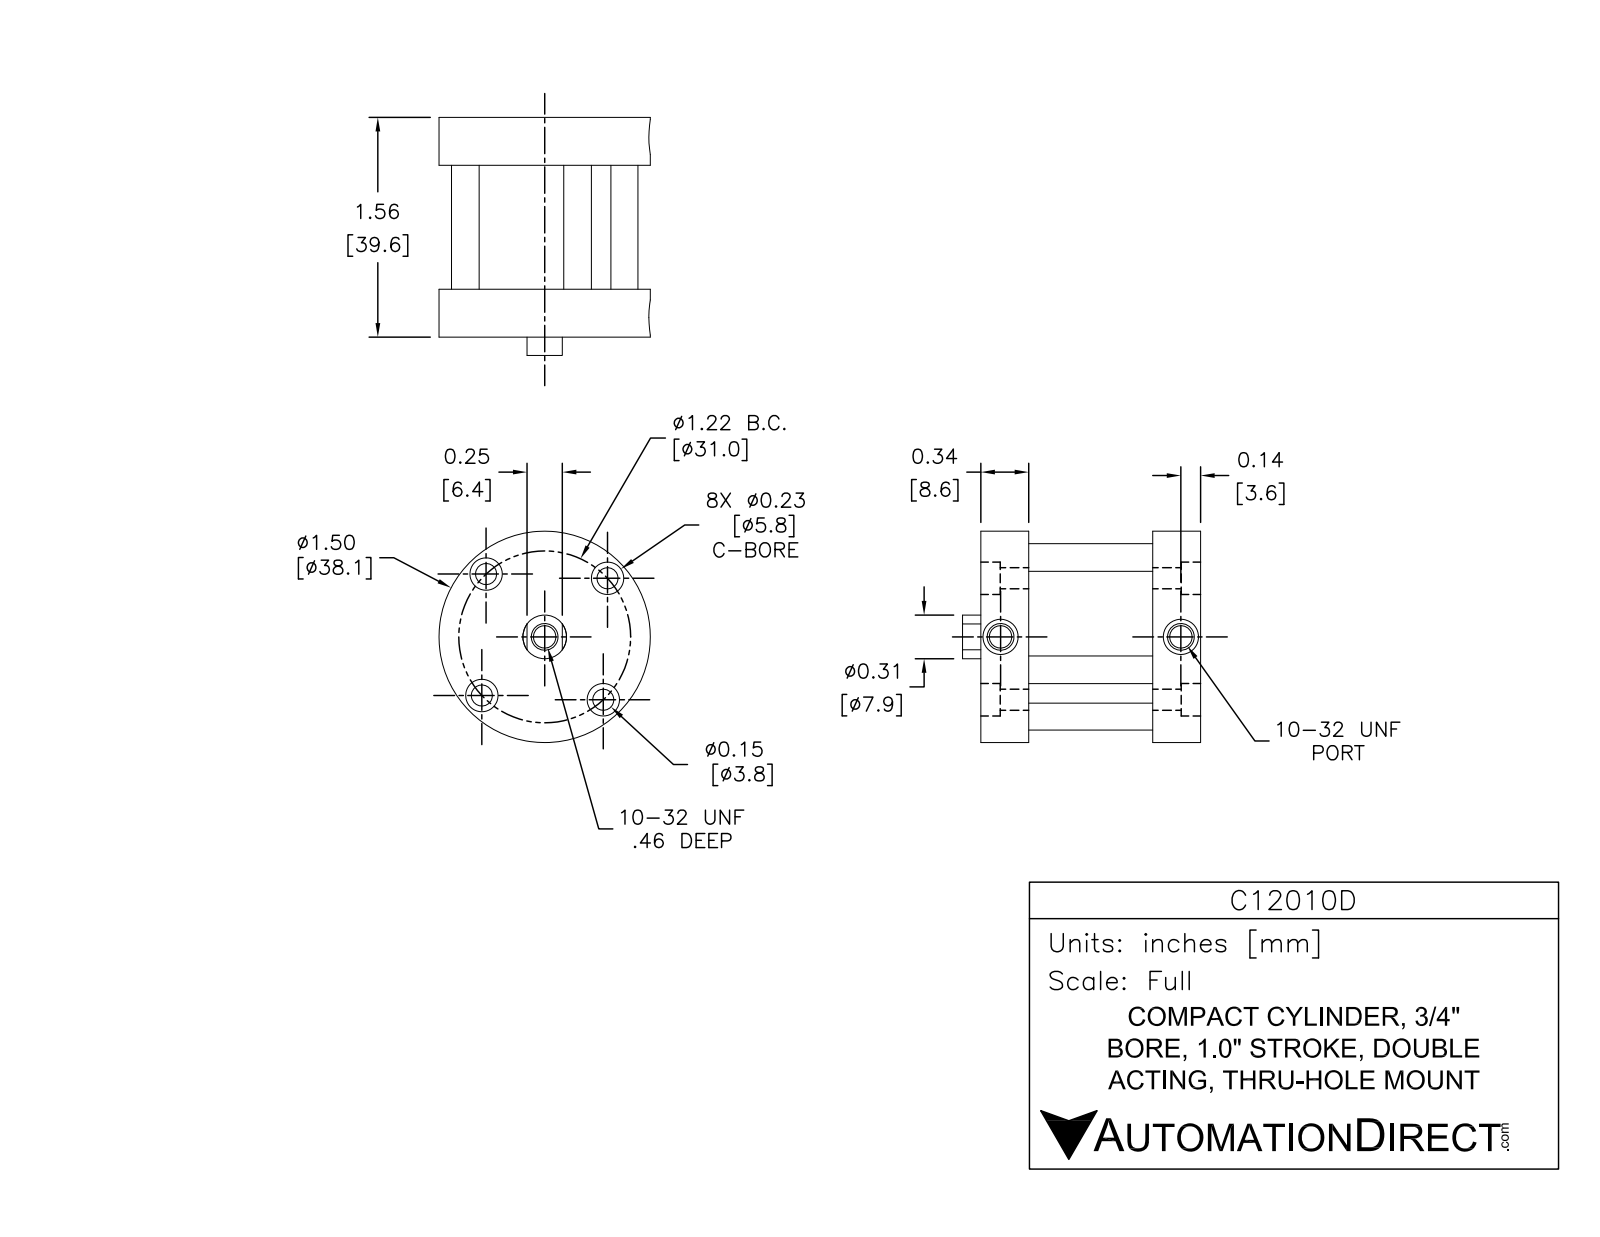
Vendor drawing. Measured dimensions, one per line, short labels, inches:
name: C12010D-FO1_BM_r; C12010D; C12010D-FO1_BM_rod; C12010D-rod_part (+3 more)
written by: SolidWorks 2014 (AUTOMOTIVE_DESIGN)
unit: in
bodies: 9 solids, 165 faces (51 planar, 104 cylindrical, 10 other)
size: 1.69 × 1.5 × 1.5
volume: 1.397 in³; area: 26.9 in²
holes: 4× ⌀0.136, 4× ⌀0.156, 4× ⌀0.235, 3× ⌀0.156, 2× ⌀0.313, 1× ⌀0.31, 1× ⌀0.312, 1× ⌀0.75, 1× ⌀0.812
bosses: 4× ⌀0.272, 1× ⌀1.5
face distances: 0.17, 1.22, 1.05, 1.56, 0.34, 0.34, 0.88, 1.22, 1.39, 1.39
hole spacings: 0.61, 0.863, 0.331, 0.596, 1.065, 1.174, 1.22, 1.28
